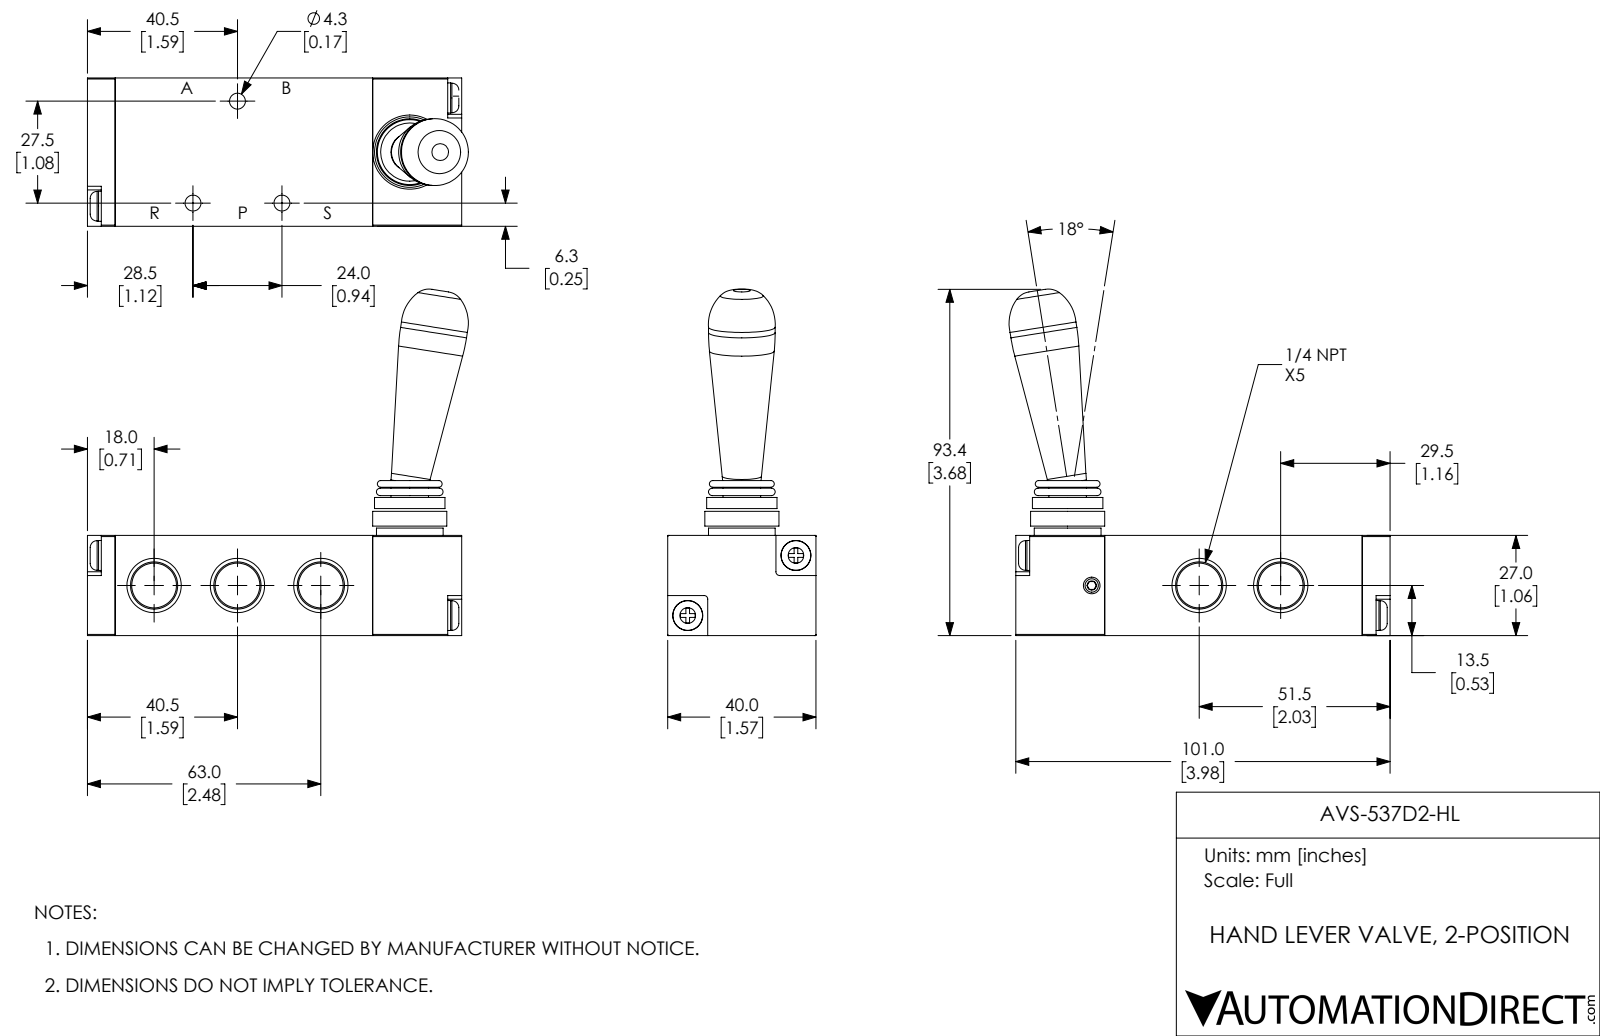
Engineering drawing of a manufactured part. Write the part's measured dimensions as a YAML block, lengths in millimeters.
part_name: "AVS-537D2-HL"
step_written_by: "SolidWorks 2017 (AUTOMOTIVE_DESIGN)"
units: millimeters
bodies: {solids: 4, faces: 223, planar: 118, cylindrical: 57, other: 48}
overall_size: [102.8, 93.4, 40]
volume: 111600
surface_area: 29030
round_holes:
  - {diameter: 4.3, count: 3}
  - {diameter: 4.5, count: 1}
  - {diameter: 18, count: 1}
round_bosses_or_shafts:
  - {diameter: 8.1, count: 4}
  - {diameter: 8, count: 4}
  - {diameter: 20, count: 1}
  - {diameter: 19, count: 1}
  - {diameter: 18, count: 1}
  - {diameter: 10.1, count: 1}
  - {diameter: 3.6, count: 1}
partial_cylinders:
  - {radius: 0.3, count: 4}
  - {radius: 1, count: 4}
face_to_face_distances: [27, 40, 69.5, 93.5, 77, 7.5, 24, 101, 2, 4]
hole_center_spacings: [30, 24, 37.1, 48.5, 60.1]
